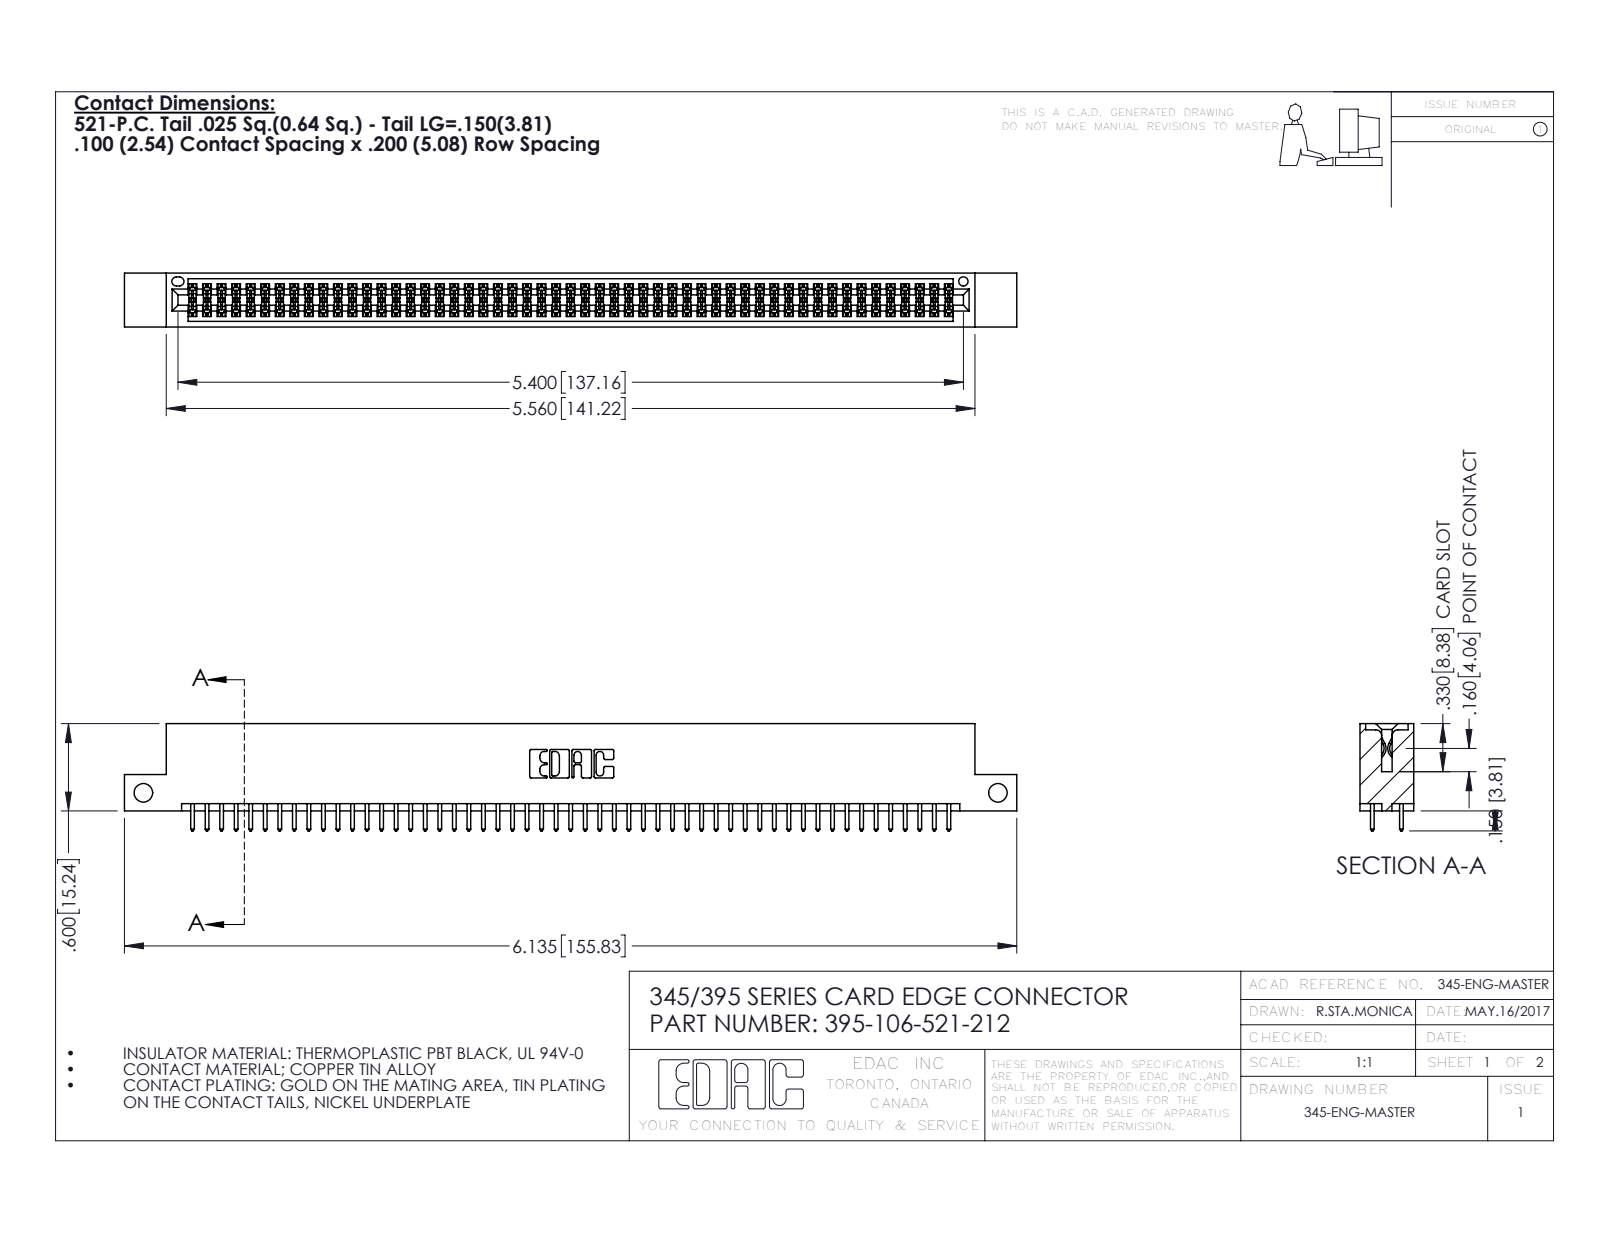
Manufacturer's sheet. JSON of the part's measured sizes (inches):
{"part_name": "345-292-001_345-293-121; 395-106-521-212; 345 Part_Flush Mounting Lugs - Side Mount", "step_written_by": "SolidWorks 2016 (CONFIG_CONTROL_DESIGN)", "units": "inches", "bodies": {"solids": 107, "faces": 5426, "planar": 3578, "cylindrical": 1848, "other": 0}, "overall_size": [6.135, 0.737, 0.37], "volume_in3": 0.922, "surface_area_in2": 34.3, "round_holes": [[0.128, 2], [0.064, 1]], "partial_cylinders_radius": [[0.006, 159], [0.01, 106], [0.01, 22], [0.007, 6], [0.031, 6], [0.026, 3], [0.014, 2], [0.019, 2]], "face_to_face_distances": [0.298, 0.072, 0.2, 0.098, 0.272, 0.025, 0.37, 0.225, 0.175, 0.149], "hole_center_spacings": [5.875]}
